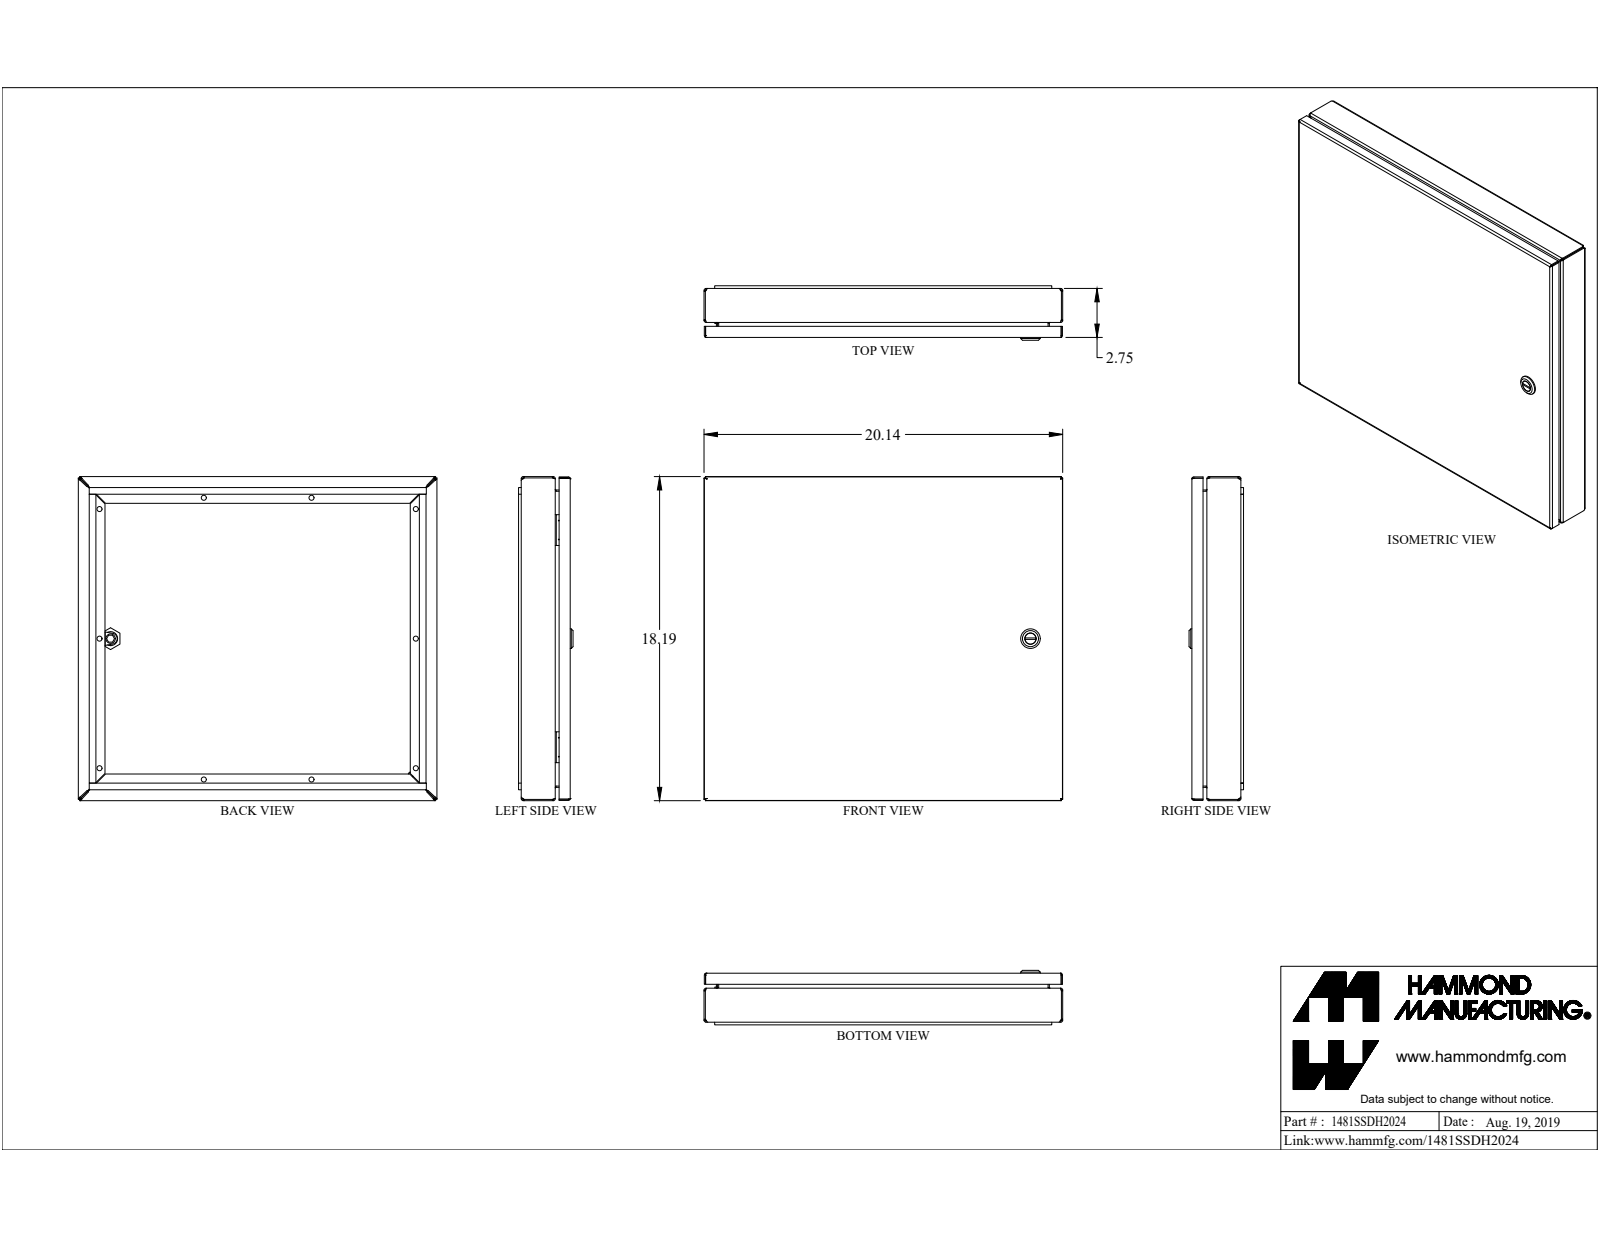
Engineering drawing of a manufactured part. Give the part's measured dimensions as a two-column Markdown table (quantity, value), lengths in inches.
| quantity | value |
| --- | --- |
| part name | 1481SSDH2024 |
| STEP written by | SolidWorks 2019 (CONFIG_CONTROL_DESIGN) |
| units | inches |
| bodies | 24 solids, 620 faces (374 planar, 149 cylindrical, 97 other) |
| overall size | 20.14 × 18.19 × 3.06 |
| volume | 68.59 in³ |
| surface area | 1 795 in² |
| round holes (diameter × count) | 0.281 × 10, 0.172 × 1, 0.197 × 1, 0.24 × 1, 0.242 × 1, 0.387 × 1, 0.5 × 1, 0.63 × 1, 0.768 × 1 |
| round bosses / shafts (diameter × count) | 1.1 × 1, 0.785 × 1, 0.625 × 1, 0.525 × 1, 0.475 × 1, 0.398 × 1, 0.356 × 1, 0.313 × 1 |
| partial cylindrical surfaces (radius × count) | 0.036 × 28, 0.108 × 28, 0.006 × 4, 0.062 × 4, 0.25 × 4, 0.499 × 4, 0.125 × 2, 0.021 × 1 |
| main face-to-face distances | 0.072, 2.578, 0.842, 1.736, 2.65, 18.118, 20.068, 2.506, 2.678, 1.836 |
| hole center spacings | 5.893, 11.922, 14.291, 16.271, 19.291, 17.764, 6.046, 7.273 |
